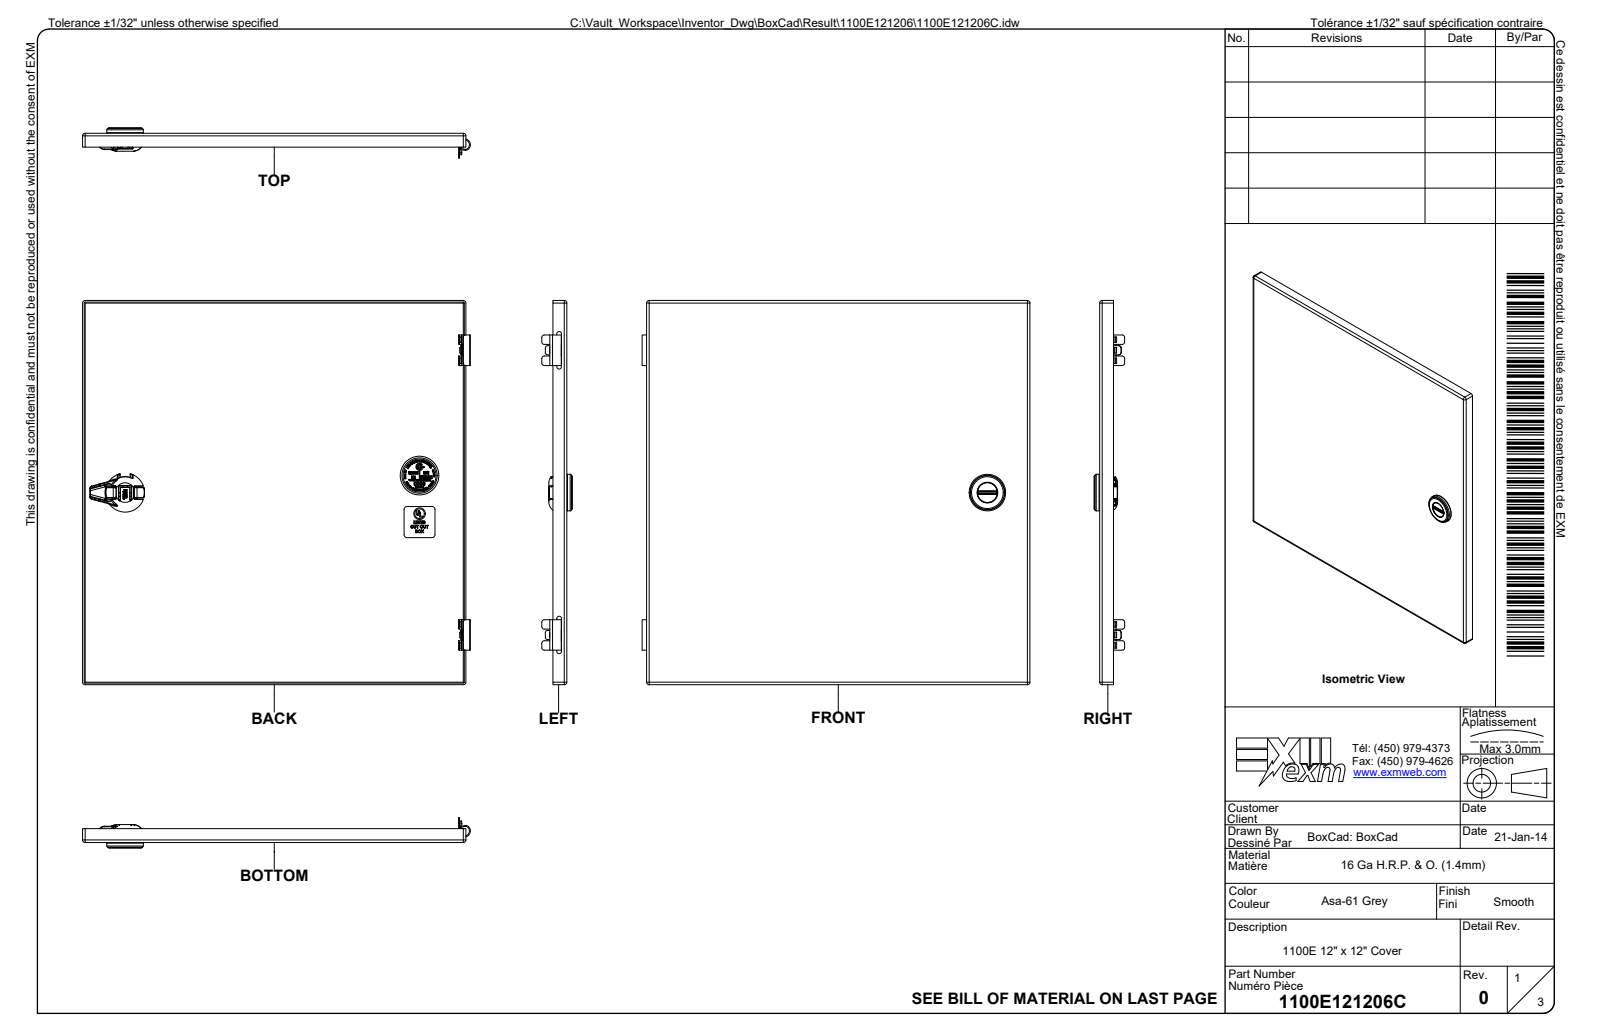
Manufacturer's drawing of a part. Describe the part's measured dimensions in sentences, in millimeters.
The part is named "1100E121206; 1100E121206B; 1100E121206B-P; 1100E121206C (+8 more)". Its 3-D file was written by "Autodesk Inventor 2024 (AUTOMOTIVE_DESIGN)". It is 8 solids with 3889 faces: 2102 planar, 696 cylindrical and 1091 other. Overall it measures 318.6 by 315 by 158.7 millimeters. Its volume is 570 300 cubic millimeters and its surface area 840 600 square millimeters. Round holes: 8 of diameter 28.6, 6 of diameter 34.9, 4 of diameter 7.4, 4 of diameter 22.2, 2 of diameter 4.5, 2 of diameter 44.5, 1 of diameter 0.8, 1 of diameter 1.1, 1 of diameter 9.5, 1 of diameter 27. Round bosses or shafts: 8 of diameter 28.6, 6 of diameter 34.9, 4 of diameter 22.2, 2 of diameter 44.5, 1 of diameter 32, 1 of diameter 31.8, 1 of diameter 30, 1 of diameter 29. Partial cylindrical surfaces (rounded edges, fillets, slot ends): 219 of radius 0.3, 22 of radius 0.8, 19 of radius 0.5, 18 of radius 2, 14 of radius 2.2, 8 of radius 2.1, 7 of radius 0.2, 4 of radius 1. The main face-to-face distances are 1.4, 303.4, 1.3, 152.8, 154.1, 151.4, 152.7, 304.8, 302, 151. The hole center spacings are 43, 48.3, 90.6, 138.2, 254, 95.3, 107.8, 134.6.
